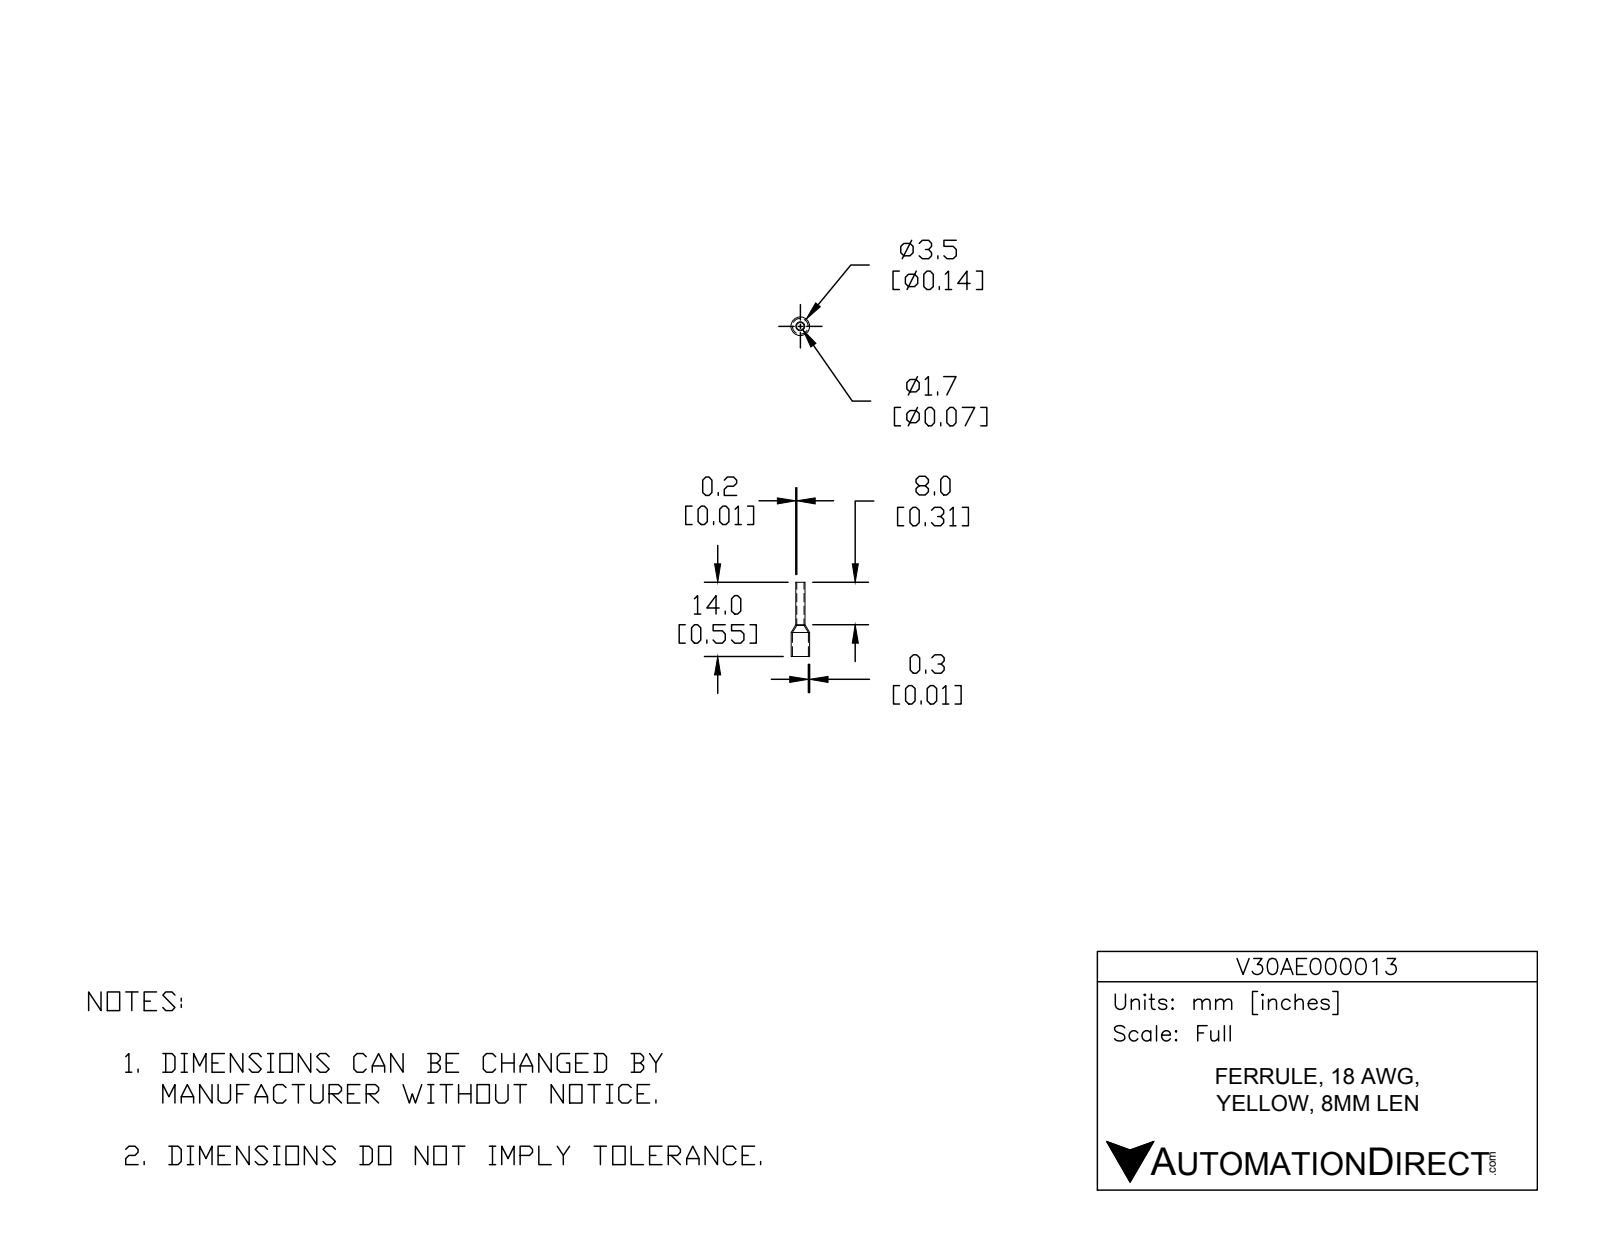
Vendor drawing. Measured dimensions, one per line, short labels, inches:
name: V30AE000013
written by: SolidWorks 2017 (AUTOMOTIVE_DESIGN)
unit: in
bodies: 1 solid, 14 faces (2 planar, 8 cylindrical, 4 other)
size: 0.551 × 0.138 × 0.138
volume: 0.001 in³; area: 0.308 in²
holes: 1× ⌀0.055, 1× ⌀0.118
bosses: 1× ⌀0.138, 1× ⌀0.067
face distances: 0.551
